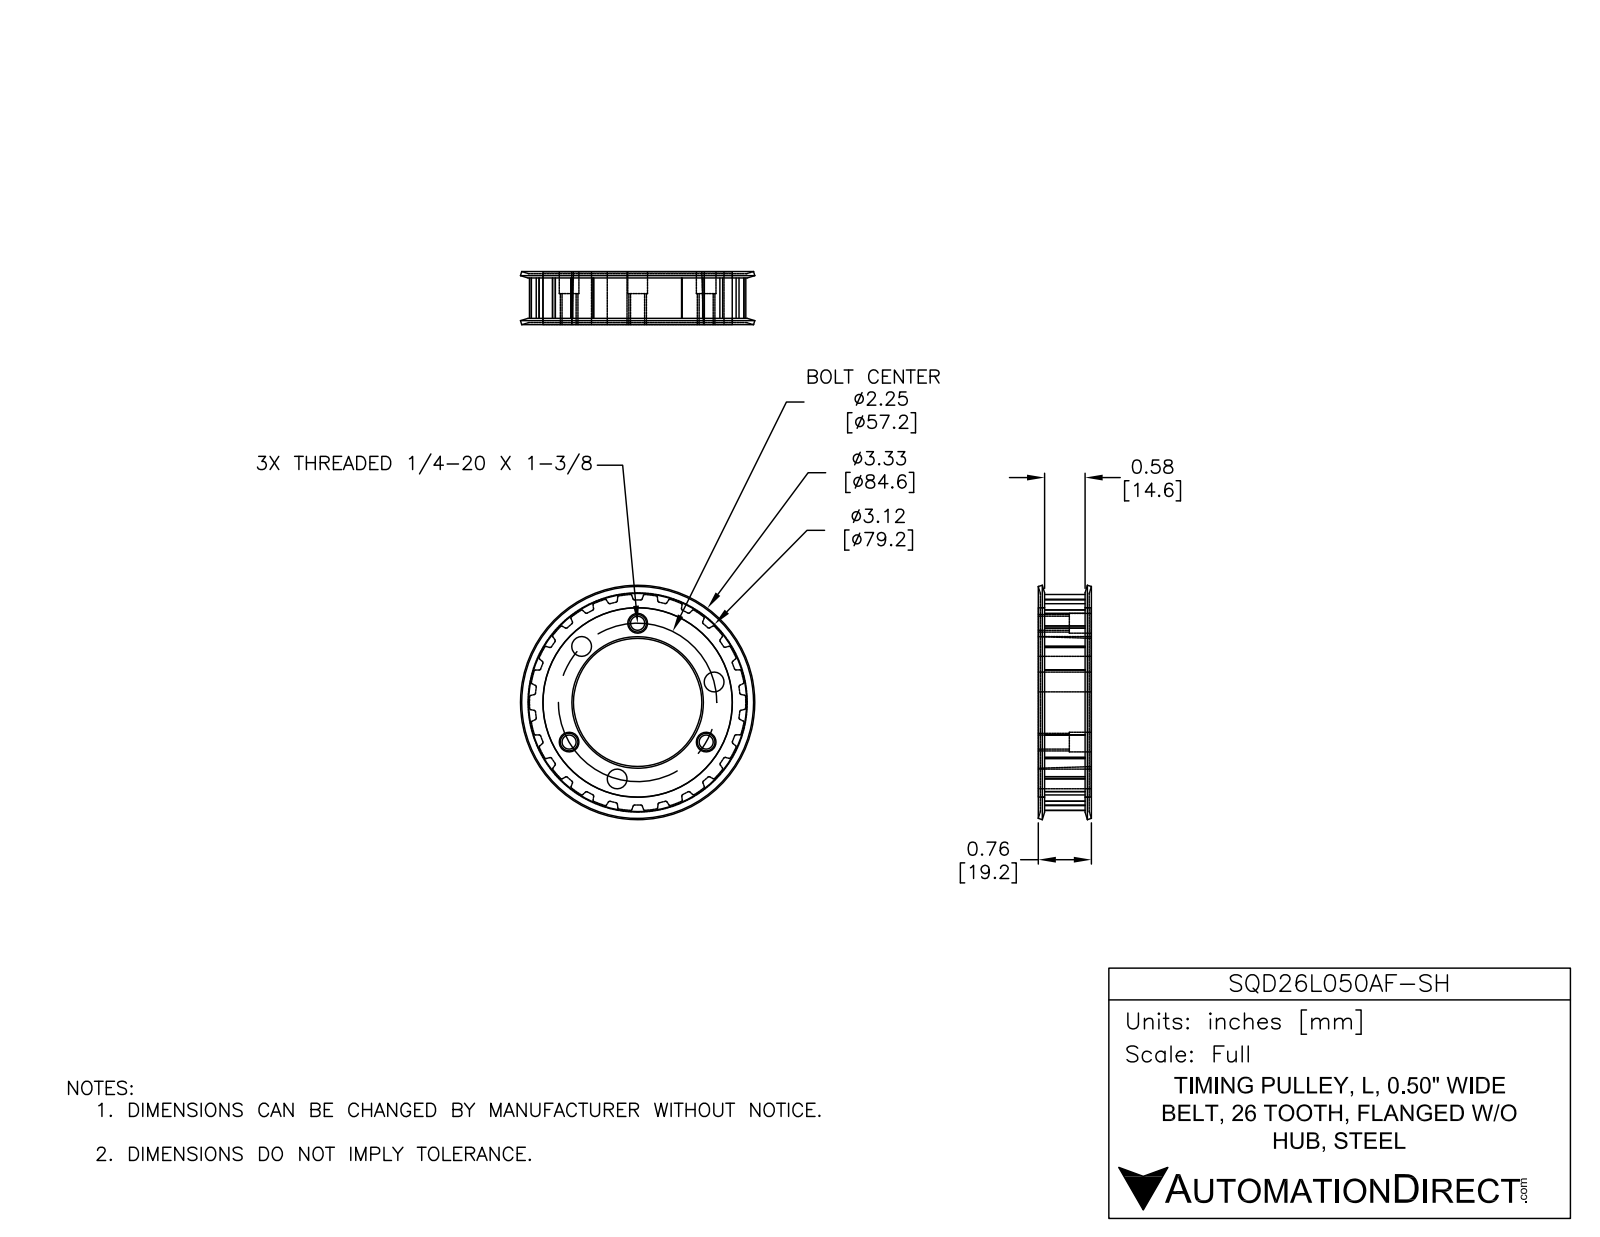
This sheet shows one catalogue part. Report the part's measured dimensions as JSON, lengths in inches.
{"part_name": "SQD26L050AF-SH", "step_written_by": "SolidWorks 2018 (AUTOMOTIVE_DESIGN)", "units": "inches", "bodies": {"solids": 4, "faces": 280, "planar": 89, "cylindrical": 177, "other": 14}, "overall_size": [3.33, 3.33, 0.755], "volume_in3": 3.189, "surface_area_in2": 48.59, "round_holes": [[0.28, 6], [0.2, 3], [2.692, 1]], "round_bosses_or_shafts": [[2.689, 1]], "partial_cylinders_radius": [[0.015, 52], [0.02, 52], [1.537, 1]], "face_to_face_distances": [0.06, 0.635, 0.575, 0.663, 0.088, 0.087, 0.662, 0.75, 0.027, 0.722], "hole_center_spacings": [1.125, 0.861, 1.949, 1.95, 2.231, 0.861, 1.126, 1.369]}
